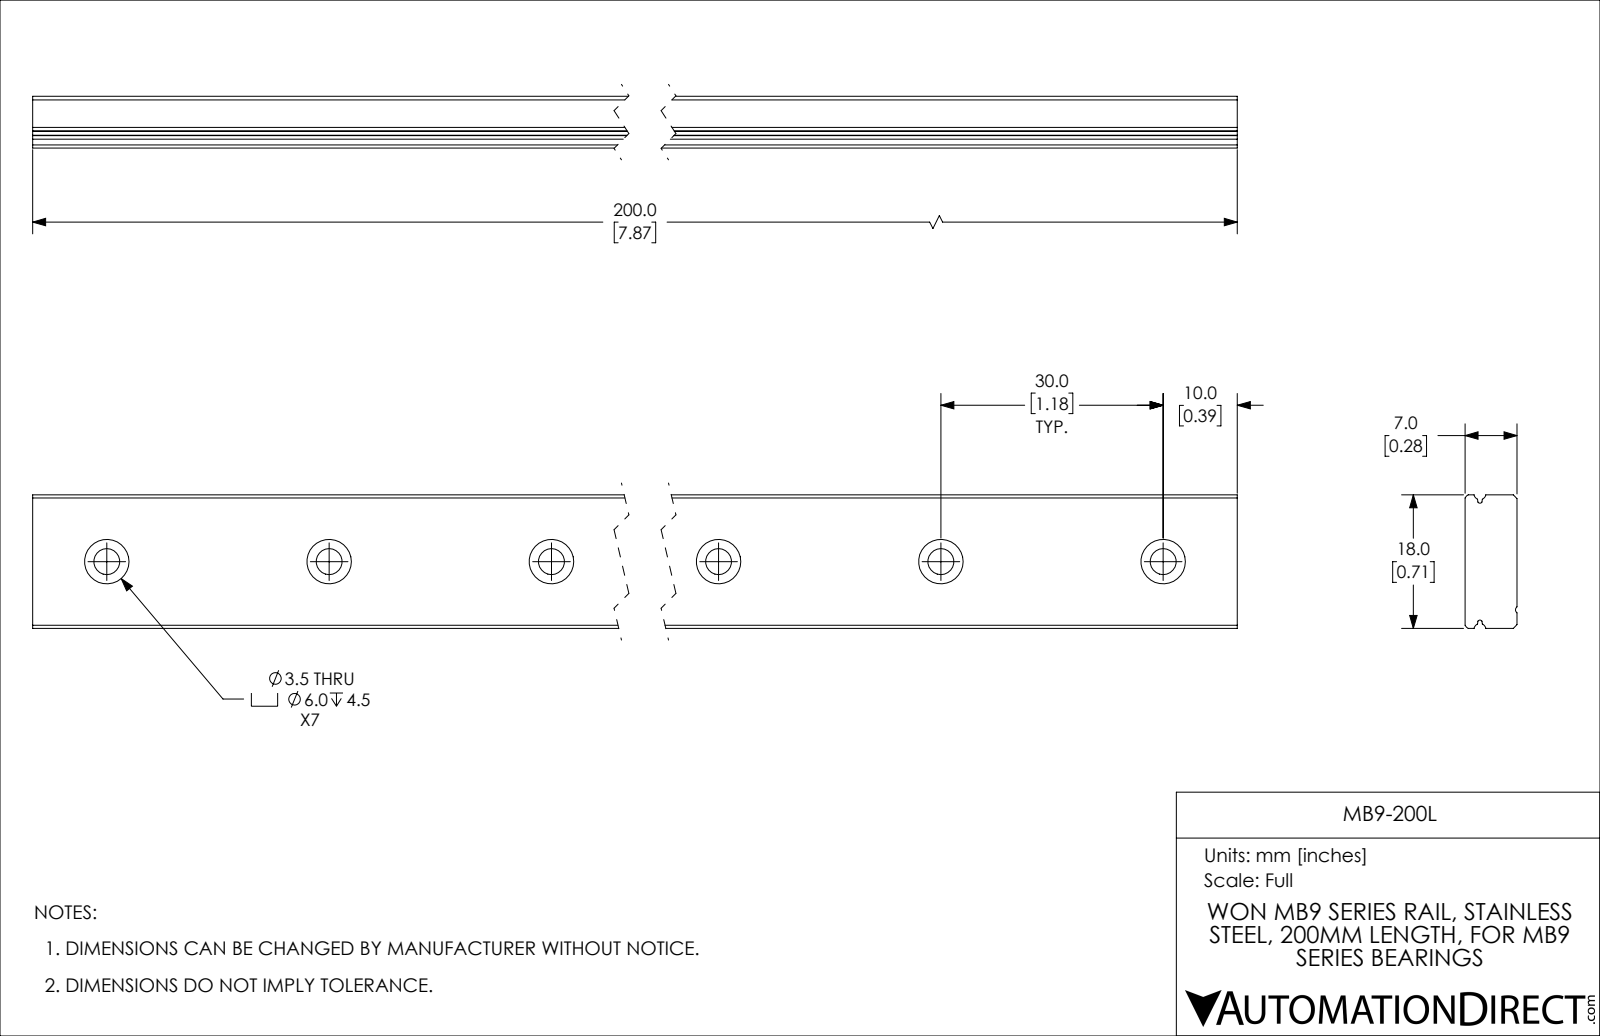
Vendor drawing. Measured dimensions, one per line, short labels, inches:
name: MB9-200L
written by: SolidWorks 2019 (CONFIG_CONTROL_DESIGN)
unit: in
bodies: 1 solid, 60 faces (22 planar, 38 cylindrical, 0 other)
size: 7.874 × 0.709 × 0.276
volume: 1.442 in³; area: 17.47 in²
holes: 7× ⌀0.138, 7× ⌀0.236
rounds: 2× R0.013, 2× R0.031, 2× R0.037, 1× R0.02
face distances: 0.276, 0.709, 0.064, 0.098, 0.177, 7.874
hole spacings: 1.181, 2.362, 3.543, 4.724, 5.906, 7.087
